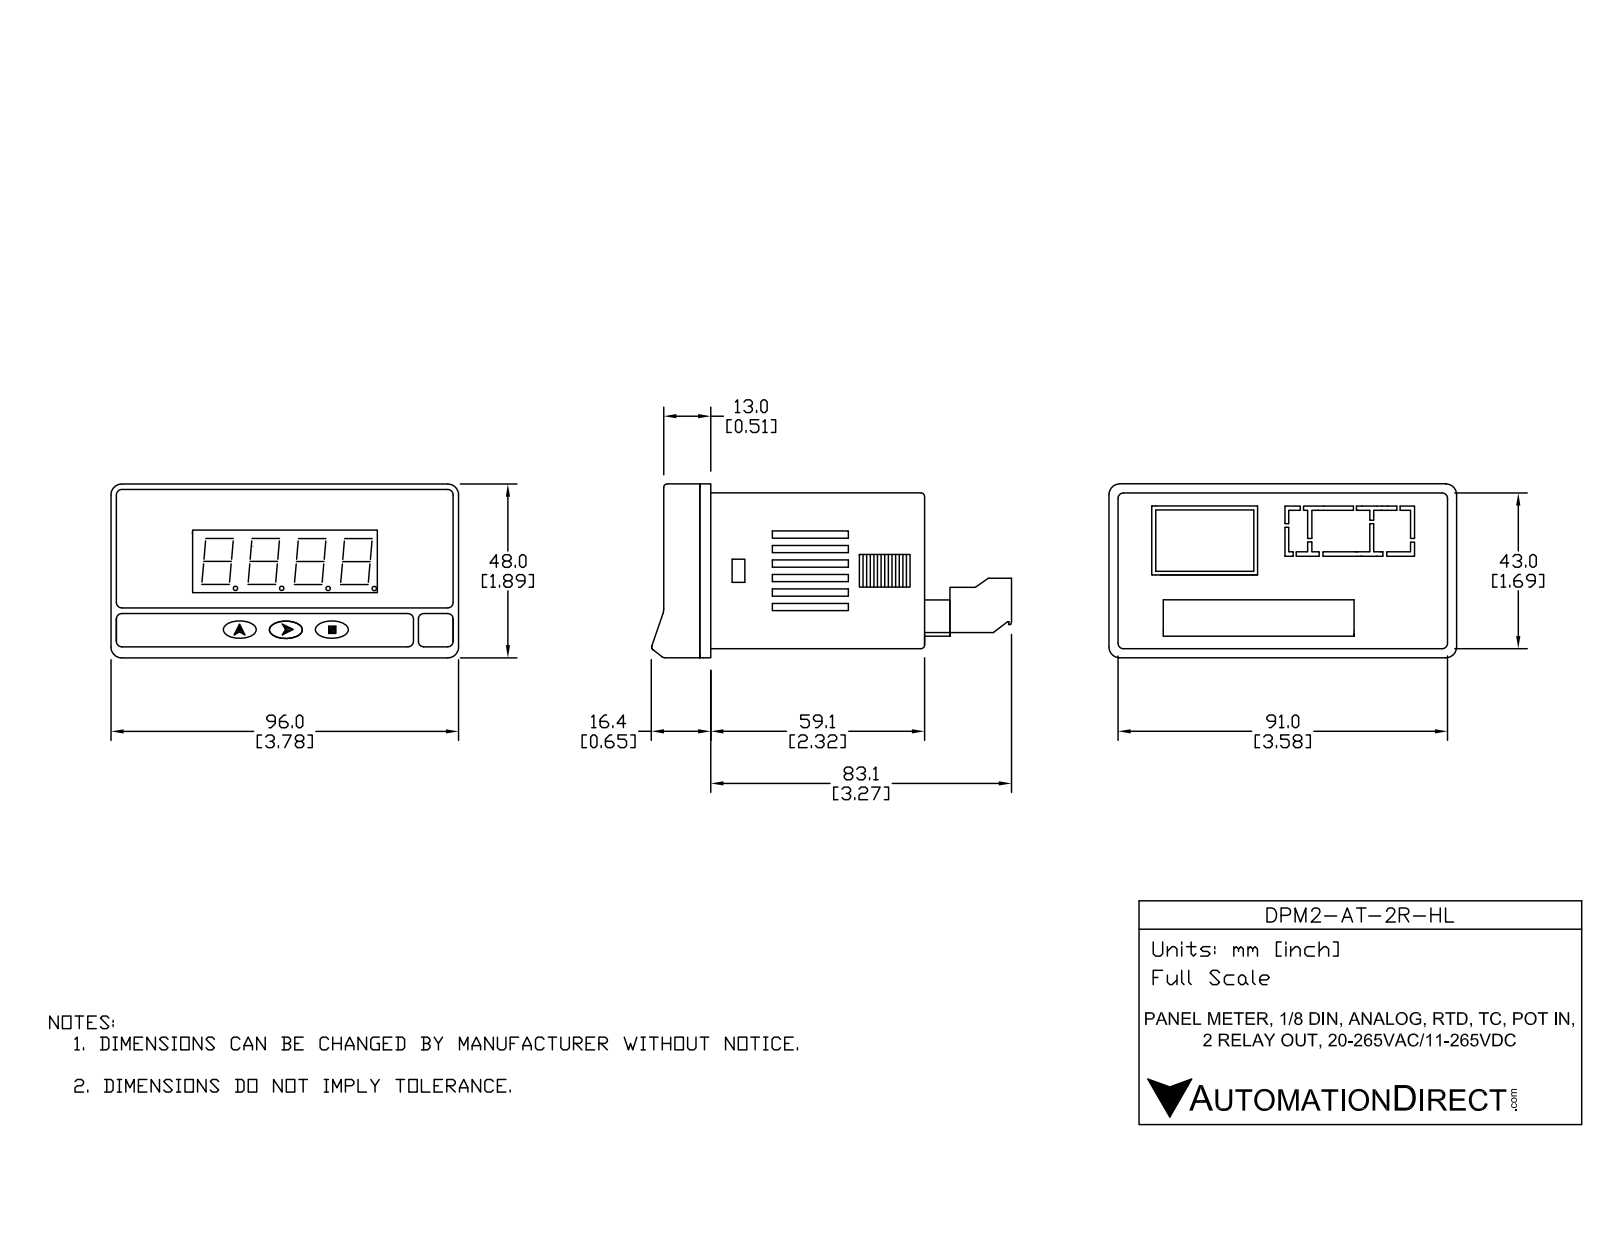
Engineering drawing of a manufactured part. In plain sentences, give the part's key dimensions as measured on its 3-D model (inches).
The part is named "DPM2-AT-2R-HL". Its 3-D file was written by "SolidWorks 2017 (AUTOMOTIVE_DESIGN)". It is 10 solids with 2096 faces: 1621 planar, 319 cylindrical and 156 other. Overall it measures 3.916 by 3.78 by 1.89 inches. Its volume is 5.519 cubic inches and its surface area 101.6 square inches. Round holes: 12 of diameter 0.039, 12 of diameter 0.079, 8 of diameter 0.078, 8 of diameter 0.118, 8 of diameter 0.152. Round bosses or shafts: 4 of diameter 0.047. Partial cylindrical surfaces (rounded edges, fillets, slot ends): 53 of radius 0.004, 24 of radius 0.012, 24 of radius 0.014, 17 of radius 0.02, 12 of radius 0.07, 12 of radius 0.072, 10 of radius 0.118, 9 of radius 0.039. The main face-to-face distances are 0.059, 1.634, 0.098, 1.693, 1.575, 1.732, 3.524, 0.433, 0.157, 2.78. The hole center spacings are 0.138, 0.276, 0.413, 0.748, 0.197, 0.197, 0.201, 0.201.
